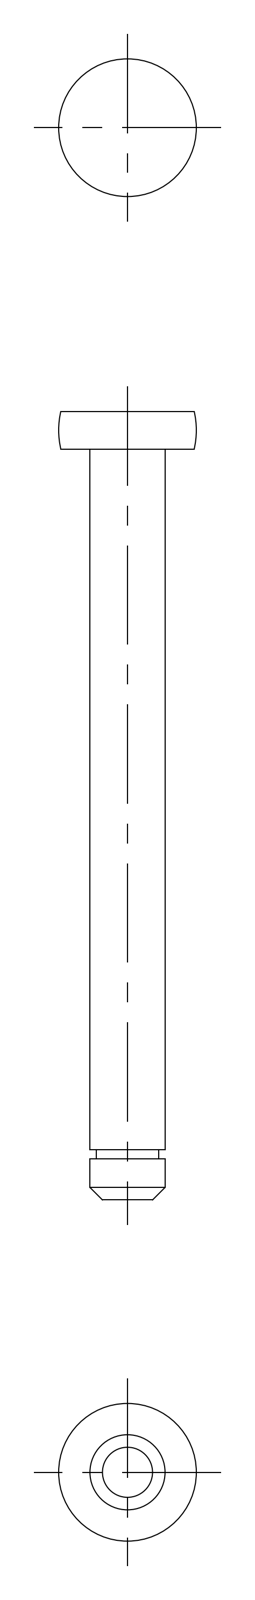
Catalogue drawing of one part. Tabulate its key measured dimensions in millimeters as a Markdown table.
| quantity | value |
| --- | --- |
| part name | TH_121SUS_6_60; shaft |
| STEP written by | SolidWorks 2015 (AUTOMOTIVE_DESIGN) |
| units | millimeters |
| bodies | 1 solid, 15 faces (5 planar, 6 cylindrical, 4 other) |
| overall size | 63 × 11 × 11 |
| volume | 1 961 mm³ |
| surface area | 1 416 mm² |
| round bosses / shafts (diameter × count) | 6 × 1, 5 × 1 |
| main face-to-face distances | 3, 60, 63, 4, 56, 59, 3.3, 0.7, 56.7, 59.7 |
